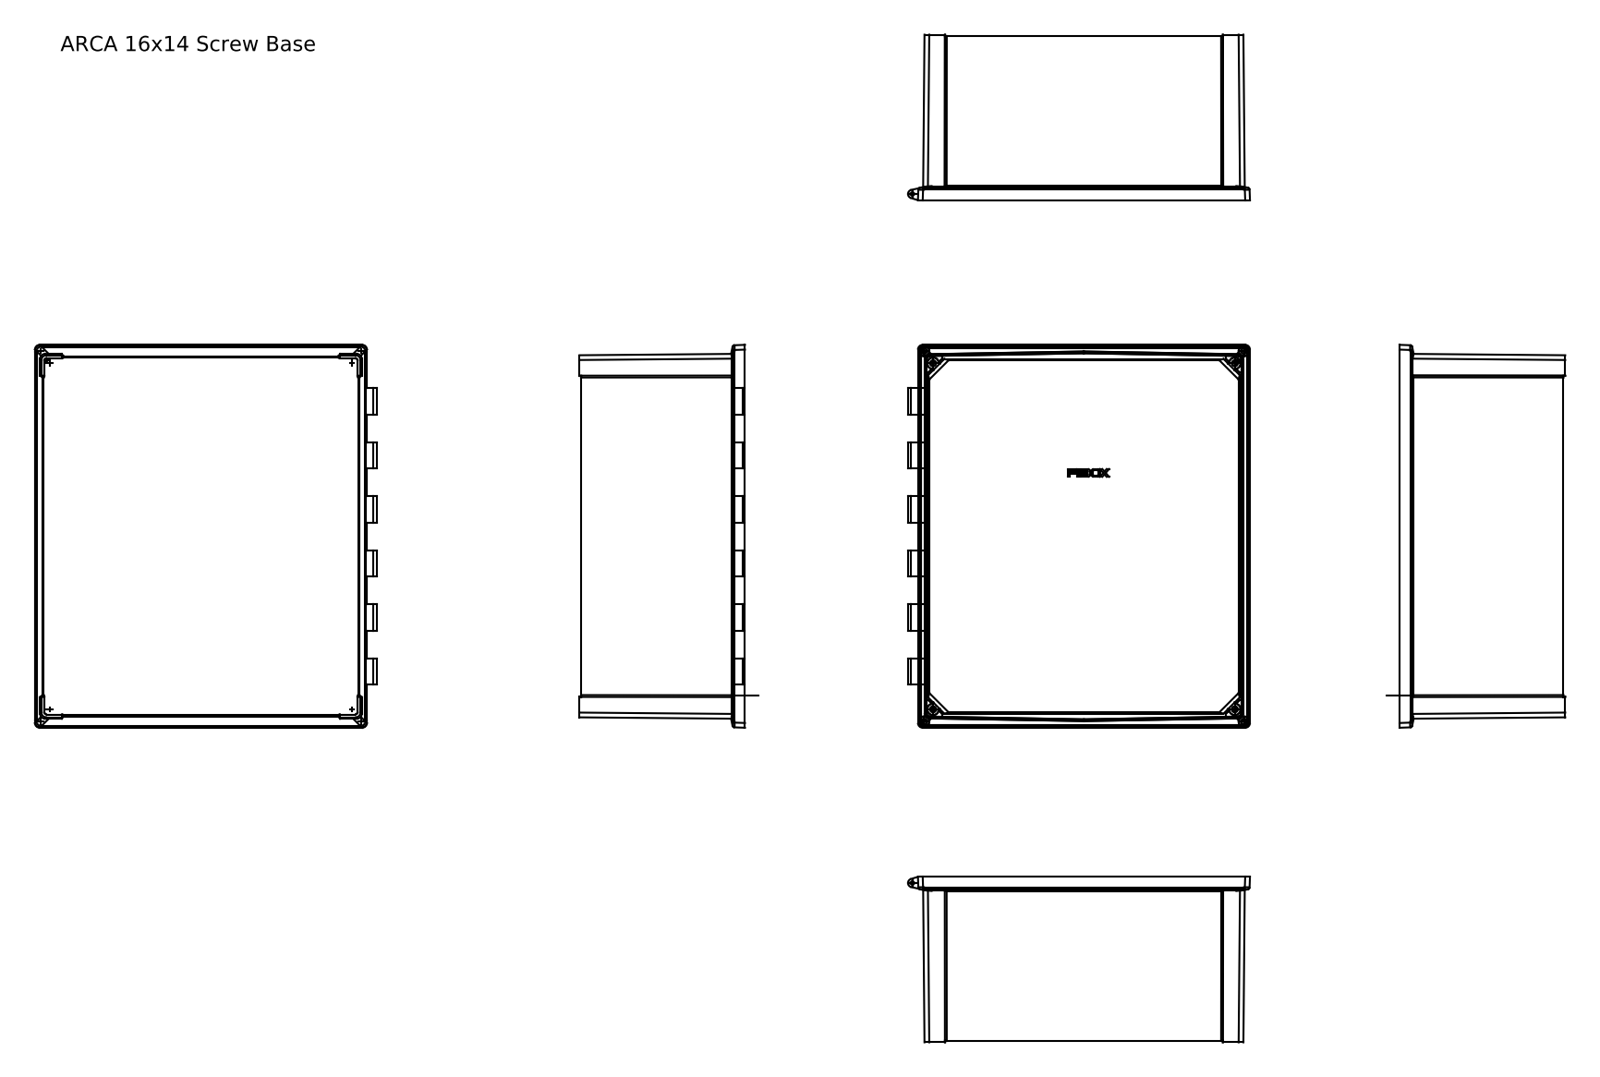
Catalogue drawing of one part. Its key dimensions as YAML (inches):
part_name: "16x14_screw_base"
step_written_by: "SolidWorks 2015 (AUTOMOTIVE_DESIGN)"
units: inches
bodies: {solids: 6, faces: 422, planar: 240, cylindrical: 44, other: 138}
overall_size: [17.437, 15.118, 7.535]
volume: 108.1
surface_area: 1463
partial_cylinders:
  - {radius: 0.217, count: 12}
  - {radius: 0.101, count: 6}
  - {radius: 0.038, count: 4}
  - {radius: 0.098, count: 4}
  - {radius: 0.138, count: 4}
  - {radius: 0.886, count: 4}
  - {radius: 1.043, count: 4}
  - {radius: 0.041, count: 2}
face_to_face_distances: [0.126, 0.142, 0.102, 0.228, 0.118, 0.16, 0.058, 0.068, 0.157, 14.57]
